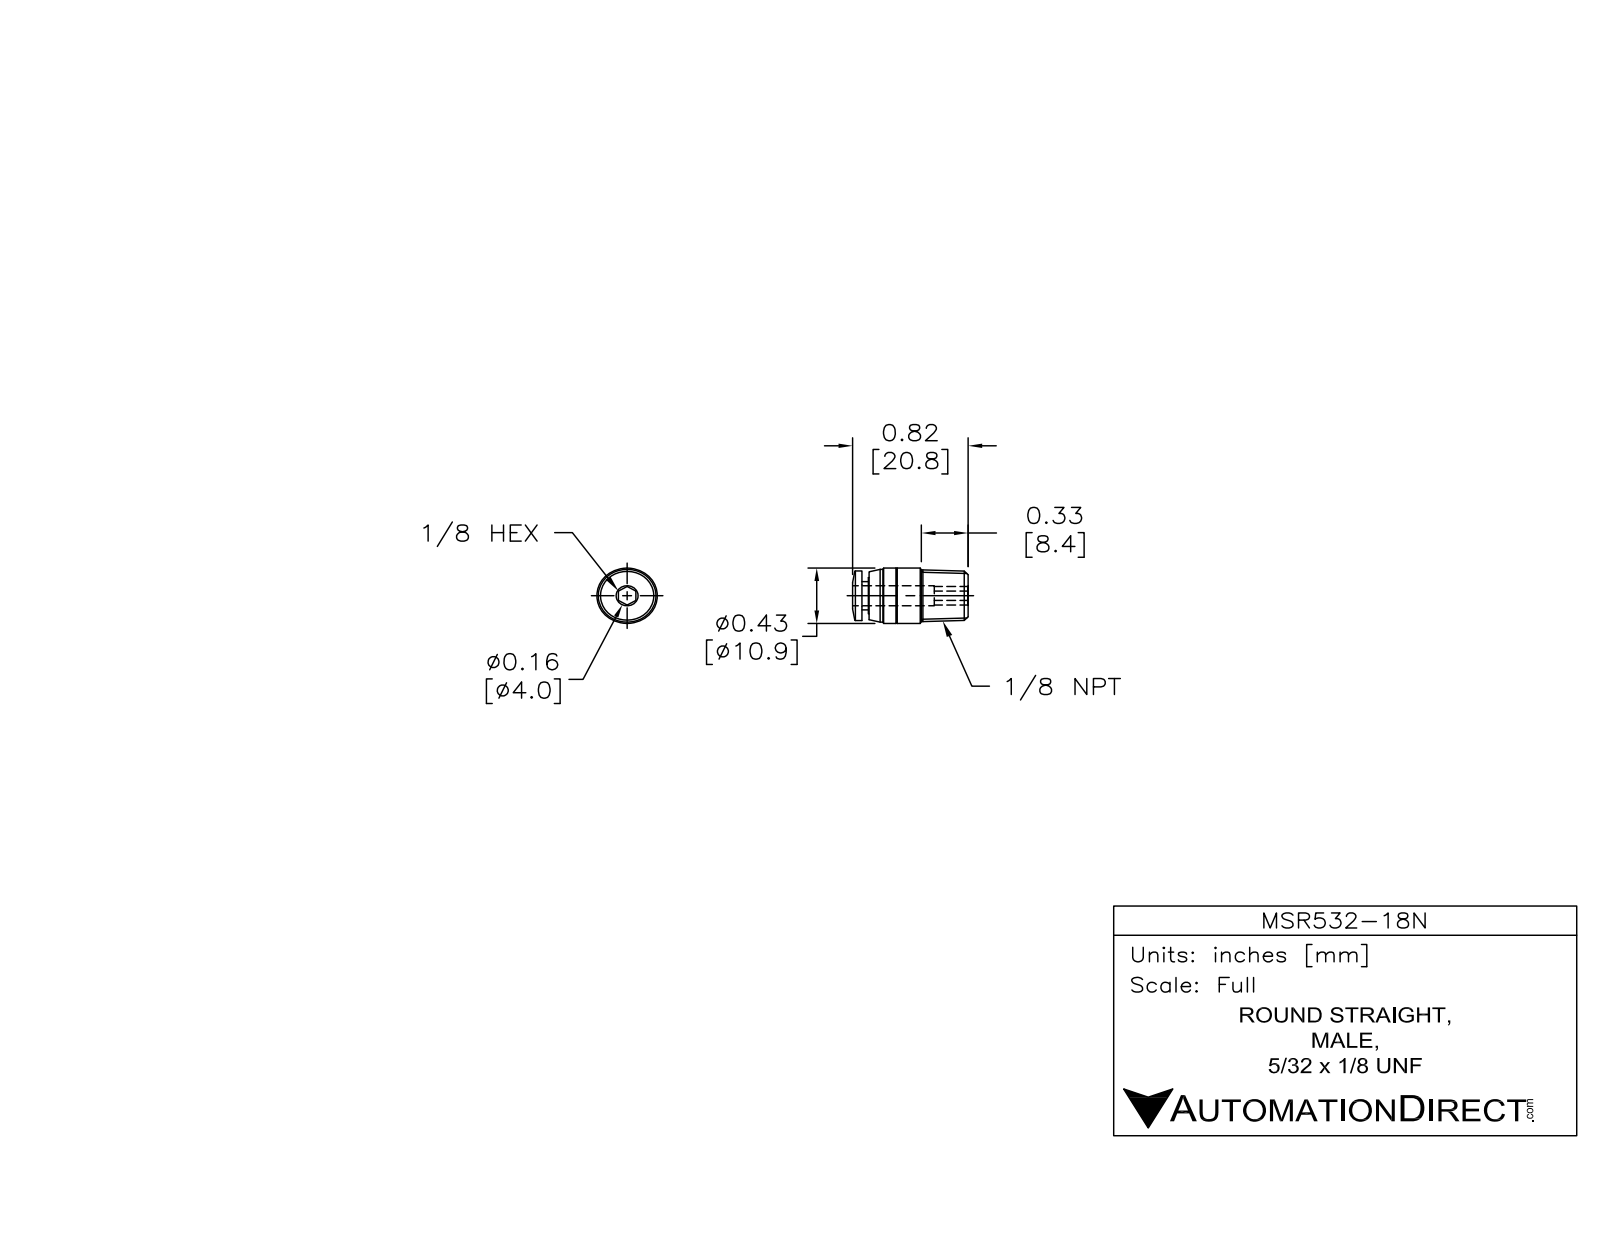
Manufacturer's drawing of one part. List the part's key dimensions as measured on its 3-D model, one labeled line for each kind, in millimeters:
Part name (STEP PRODUCT): MSR532-18N
STEP written by: SolidWorks 2015 (AUTOMOTIVE_DESIGN)
Units: millimetres
Bodies: 1 solid, 43 faces (5 planar, 16 cylindrical, 22 other)
Overall size (bounding box): 21 × 11 × 11
Volume: 1 400 mm³ · Surface area: 1 154 mm²
Round holes (diameter × count): ⌀3.2 ×1, ⌀4.3 ×1
Round bosses / shafts (diameter × count): ⌀11 ×1, ⌀10.5 ×1, ⌀9.9 ×1, ⌀7.2 ×1, ⌀5.6 ×1
Main face-to-face distances: 19.3, 18, 1.3, 18.2, 1.1, 6.2, 11.8, 11.9, 13.1
